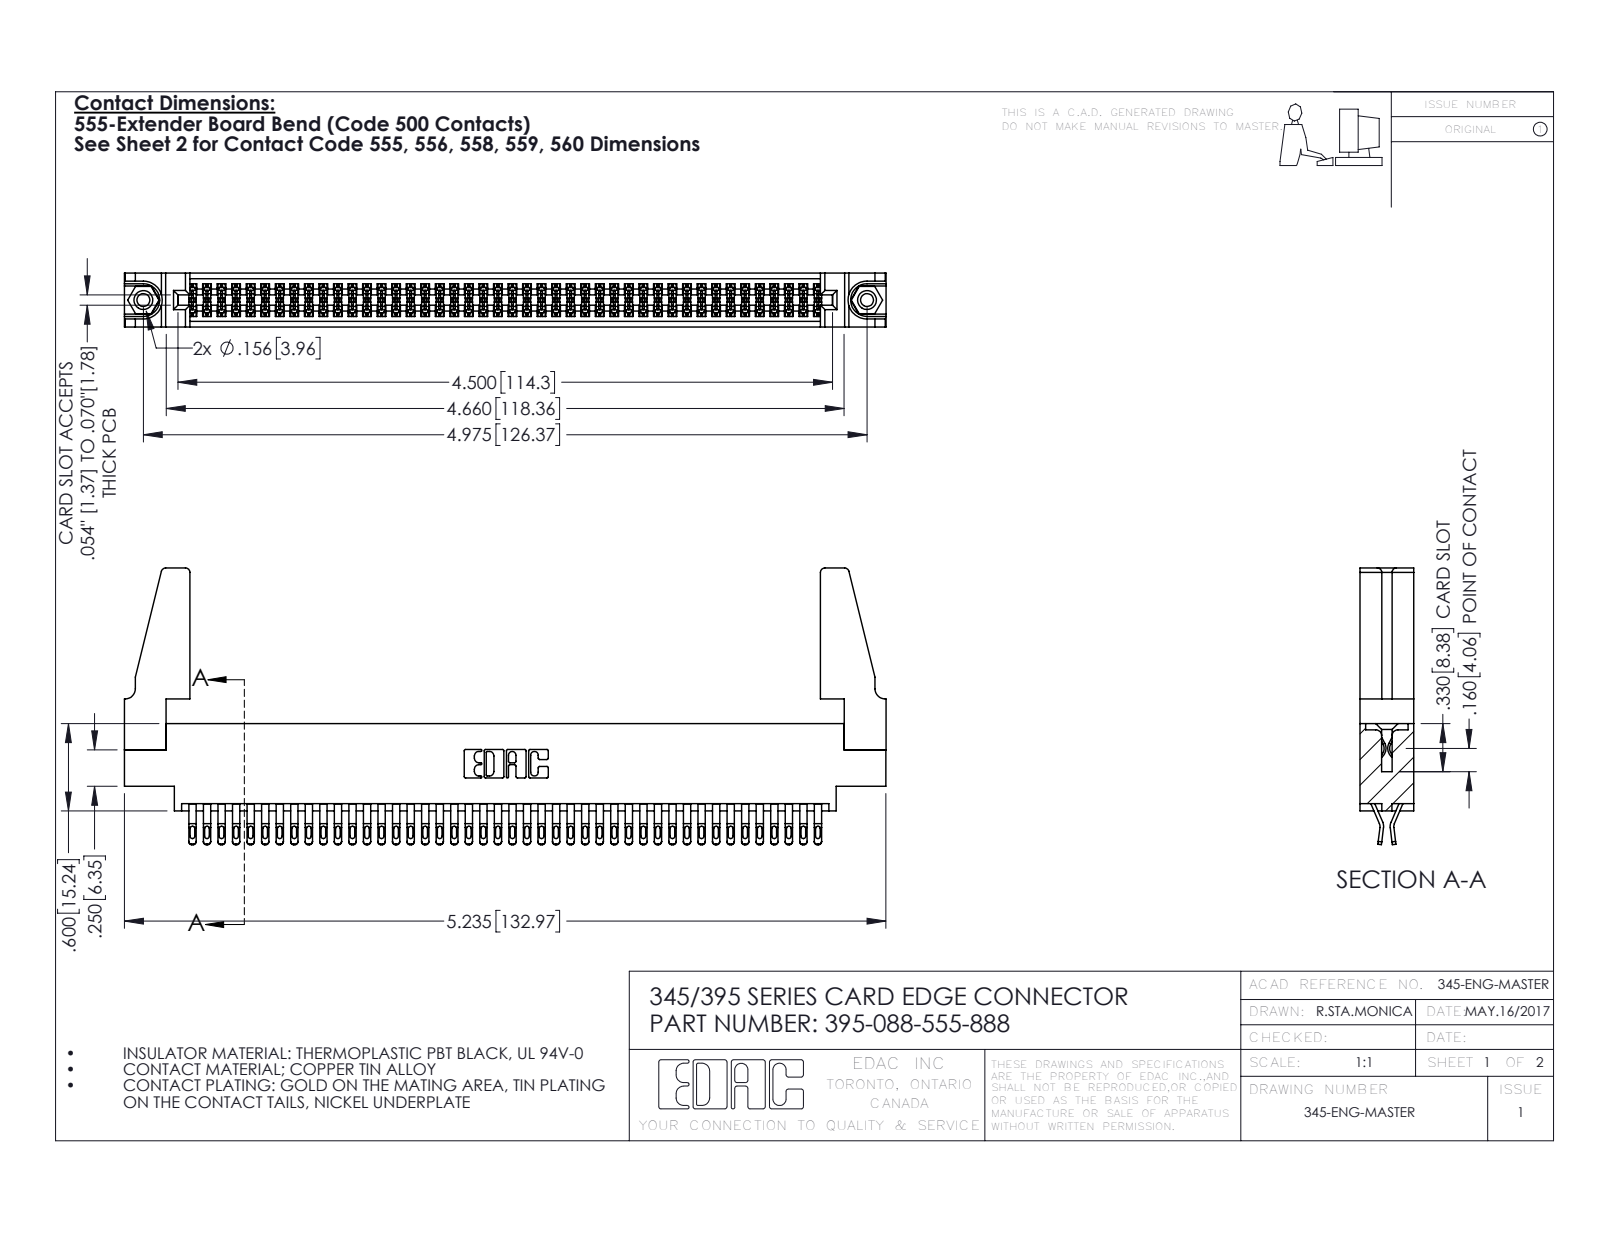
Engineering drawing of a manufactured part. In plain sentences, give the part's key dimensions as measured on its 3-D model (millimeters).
The part is named "395-088-555-888; 345-292-001_555 Tail; 345-250-001_345-250-001-102; 345 Part_0.170 Offset - 0.156 Dia-TH (+1 more)". Its 3-D file was written by "SolidWorks 2016 (CONFIG_CONTROL_DESIGN)". It is 93 solids with 5182 faces: 2884 planar, 2282 cylindrical and 16 other. Overall it measures 133 by 48.3 by 9.4 millimeters. Its volume is 16 300 cubic millimeters and its surface area 23 530 square millimeters. Round holes: 2 of diameter 2.3, 2 of diameter 3.2, 2 of diameter 4, 1 of diameter 1.6. Round bosses or shafts: 2 of diameter 3.9. Partial cylindrical surfaces (rounded edges, fillets, slot ends): 220 of radius 0.4, 176 of radius 0.5, 132 of radius 0.2, 22 of radius 0.3, 8 of radius 0.8, 6 of radius 0.2, 6 of radius 0.8, 3 of radius 0.7. The main face-to-face distances are 1.8, 7.6, 9.4, 0.6, 5.1, 2.5, 6.9, 5.7, 4.4, 3.8. The hole center spacings are 6.9, 120.4, 126.4.
